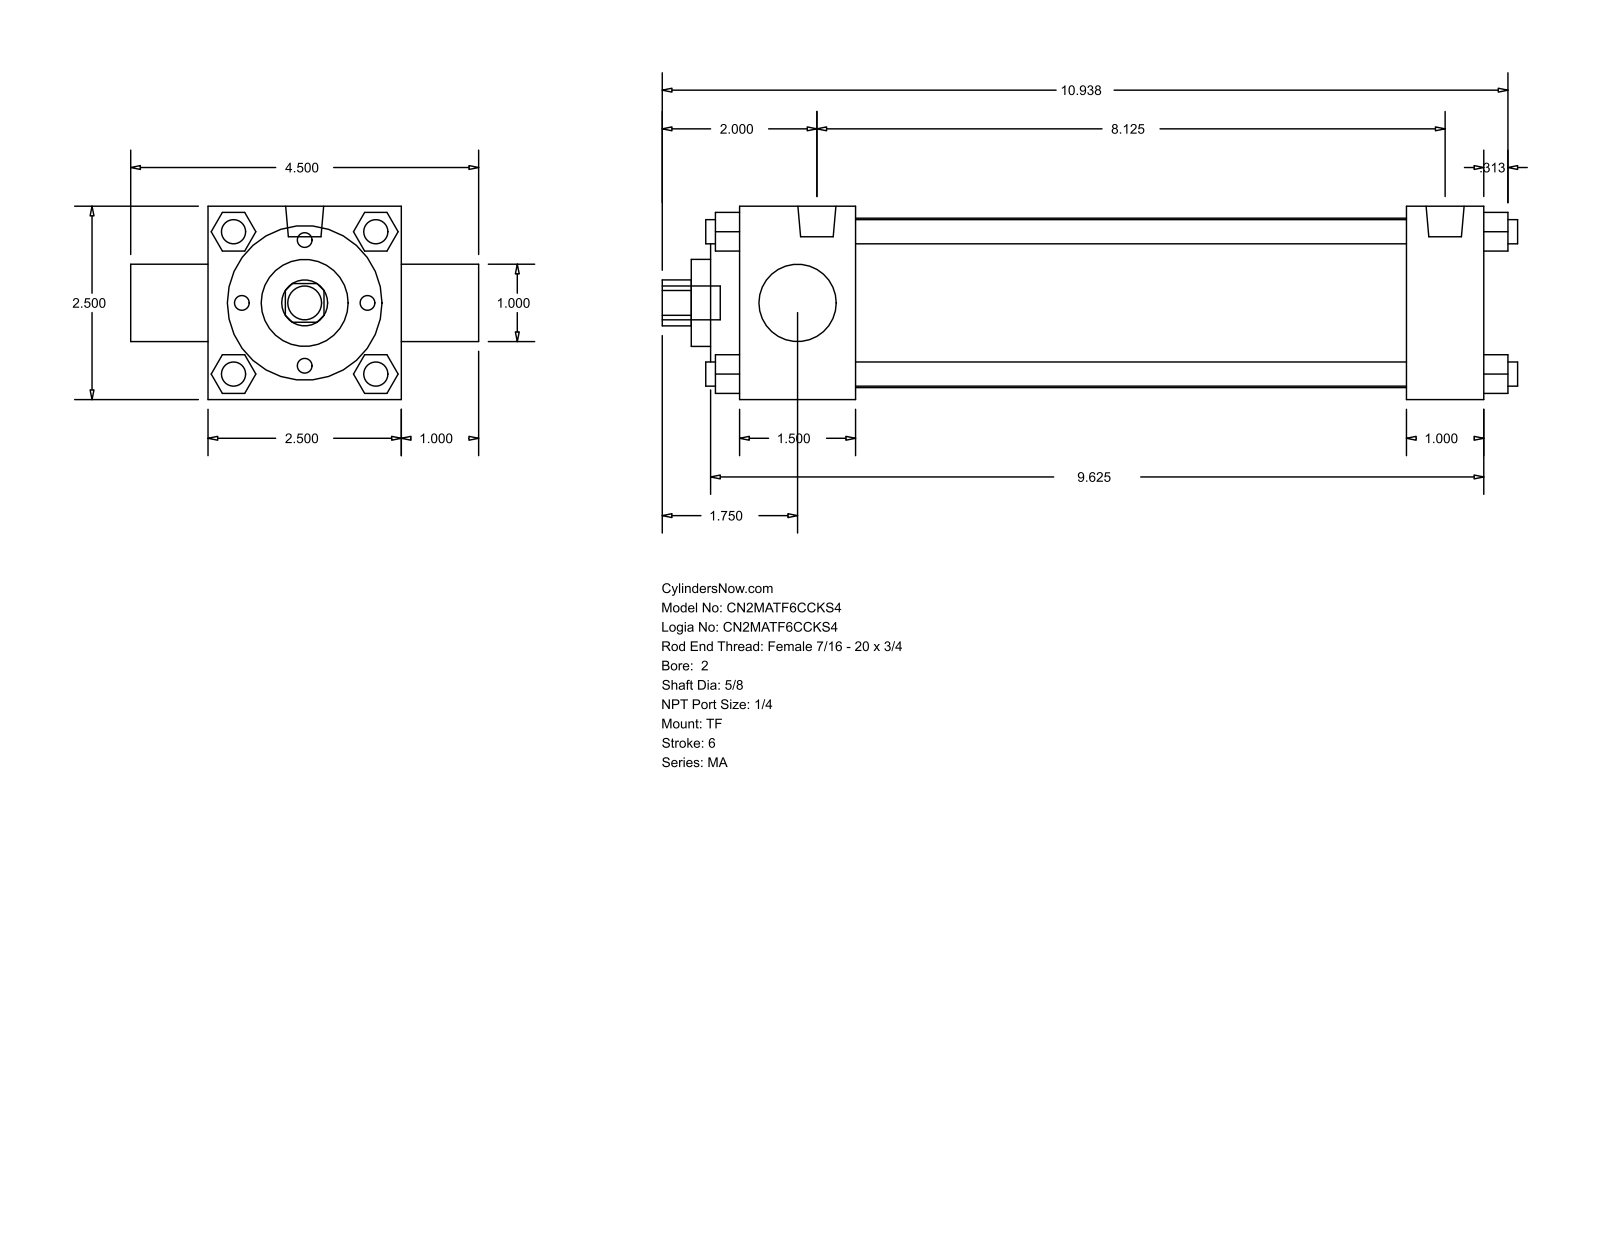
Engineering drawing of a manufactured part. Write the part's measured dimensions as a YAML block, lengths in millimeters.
part_name: "MA_TF__0200_0.625"
step_written_by: "GSSL Pune (CONFIG_CONTROL_DESIGN)"
units: millimeters
bodies: {solids: 0, faces: 122, planar: 93, cylindrical: 29, other: 0}
overall_size: [280.99, 114.3, 63.5]
round_holes:
  - {diameter: 15.88, count: 1}
  - {diameter: 25.4, count: 1}
  - {diameter: 28.57, count: 1}
  - {diameter: 50.8, count: 1}
  - {diameter: 55.63, count: 1}
round_bosses_or_shafts:
  - {diameter: 7.94, count: 7}
  - {diameter: 12.49, count: 2}
  - {diameter: 11.11, count: 1}
partial_cylinders:
  - {radius: 7.54, count: 1}
face_to_face_distances: [63.5, 38.1, 12.7, 9.52, 244.48, 219.07, 180.97, 206.38, 25.41, 47.62]
